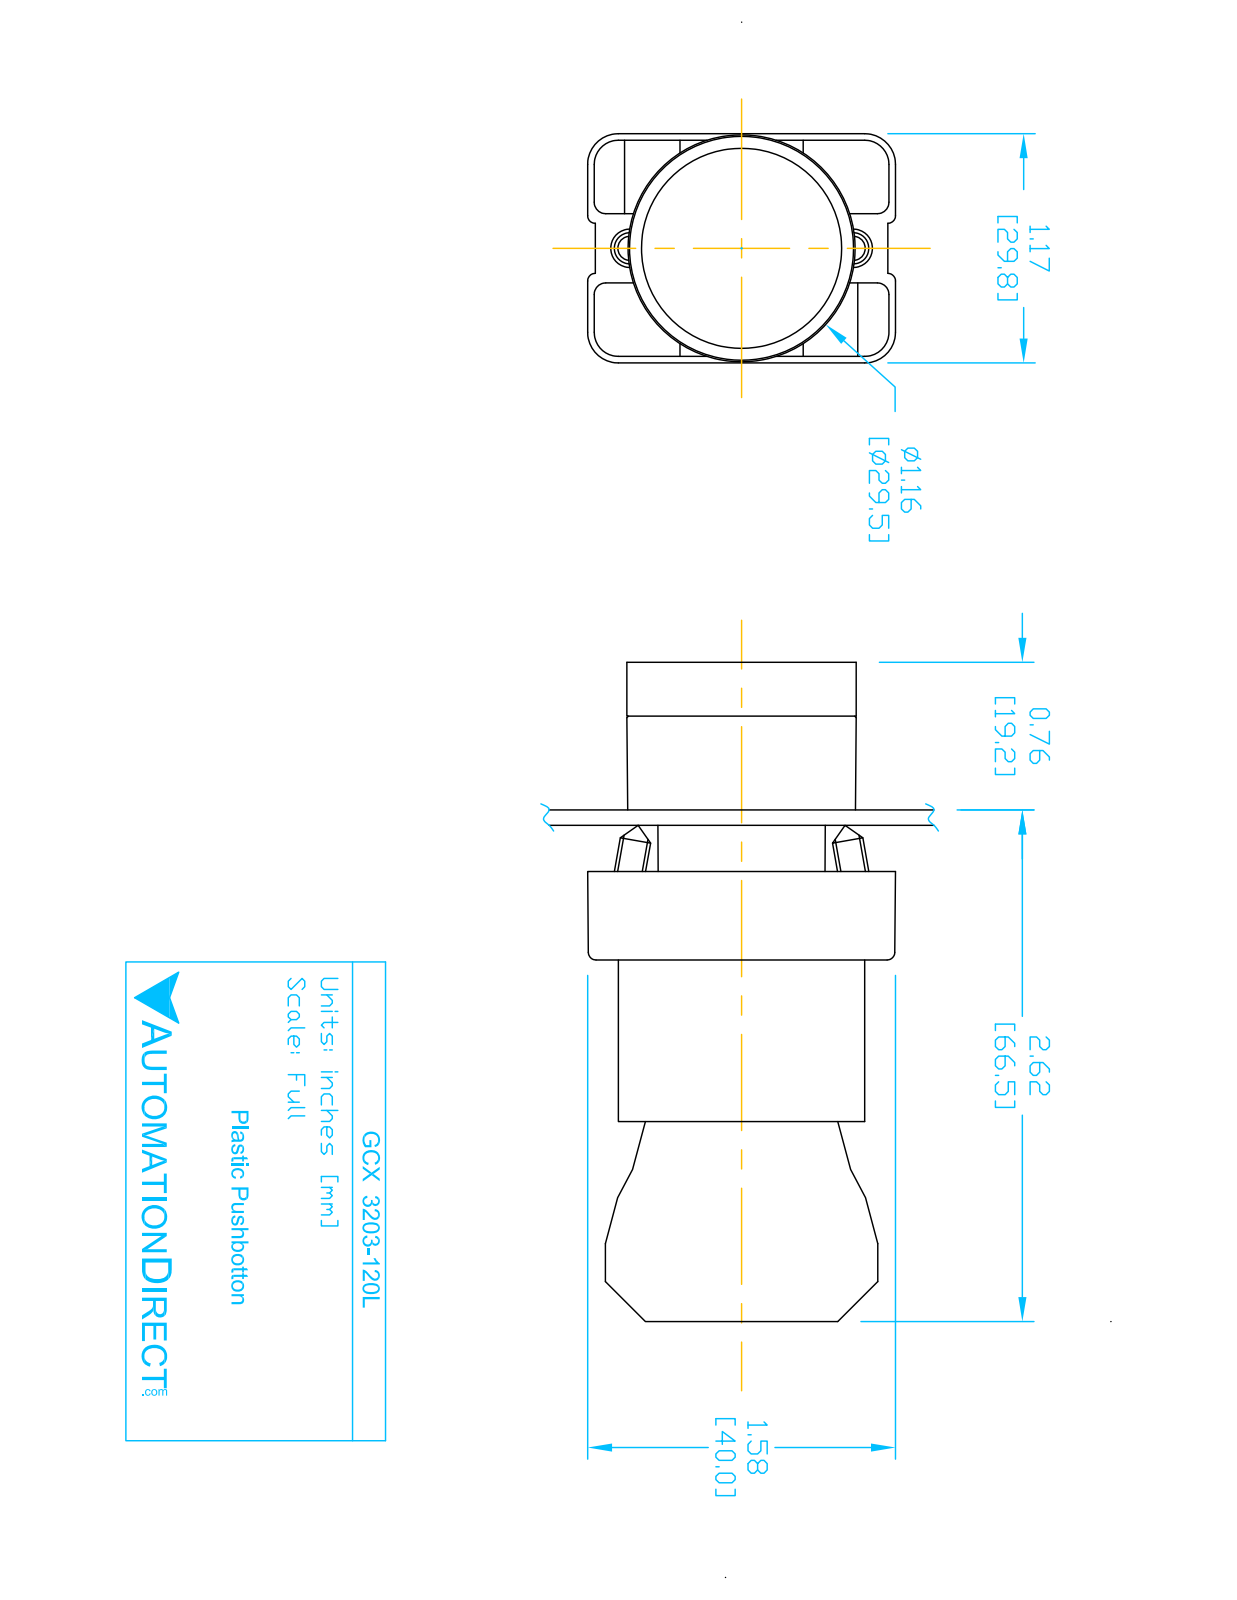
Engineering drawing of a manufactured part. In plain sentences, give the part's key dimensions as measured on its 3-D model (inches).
The part is named "ECX3029-2; GCX3203-120L; GCX3203L OPERATOR; ECX1050 (+1 more)". Its 3-D file was written by "SolidWorks 2016 (AUTOMOTIVE_DESIGN)". It is 8 solids with 431 faces: 252 planar, 148 cylindrical and 31 other. Overall it measures 3.319 by 1.581 by 1.177 inches. Its volume is 2.794 cubic inches and its surface area 38.77 square inches. Round holes: 2 of diameter 0.079, 2 of diameter 0.124, 2 of diameter 0.13, 1 of diameter 0.087, 1 of diameter 0.197, 1 of diameter 0.469, 1 of diameter 0.878, 1 of diameter 0.888, 1 of diameter 1.024. Round bosses or shafts: 4 of diameter 0.157, 1 of diameter 1.175, 1 of diameter 1.004, 1 of diameter 0.945, 1 of diameter 0.856, 1 of diameter 0.78, 1 of diameter 0.504. Partial cylindrical surfaces (rounded edges, fillets, slot ends): 24 of radius 0.059, 12 of radius 0.041, 12 of radius 0.124, 12 of radius 0.157, 8 of radius 0.039, 2 of radius 0.128, 1 of radius 0.02, 1 of radius 0.063. The main face-to-face distances are 0.827, 0.579, 2.02, 1.193, 1.171, 0.276, 2.295, 1.469, 0.031, 0.033. The hole center spacings are 0.236, 0.544, 0.472, 0.49.
